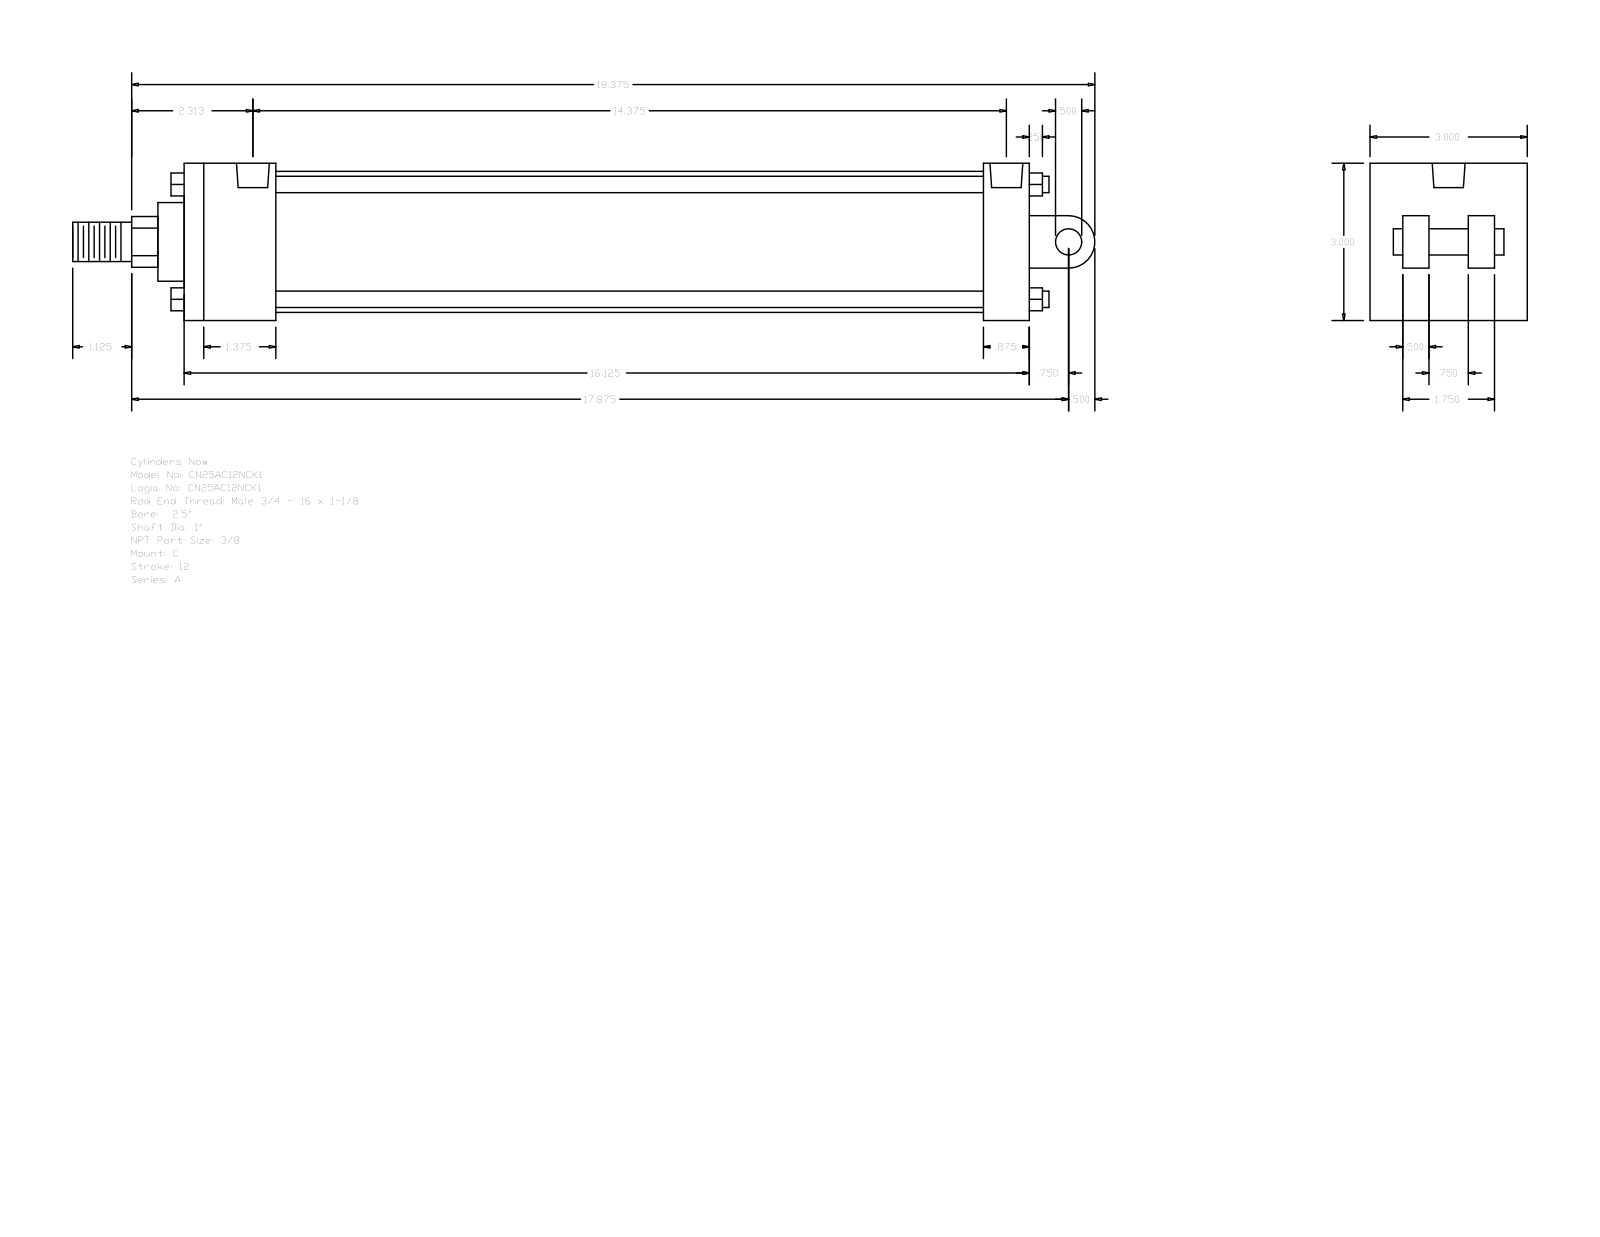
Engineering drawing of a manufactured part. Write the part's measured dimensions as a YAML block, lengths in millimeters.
part_name: "A_C__0250_1"
step_written_by: "GSSL Pune (CONFIG_CONTROL_DESIGN)"
units: millimeters
bodies: {solids: 0, faces: 135, planar: 102, cylindrical: 33, other: 0}
overall_size: [495.3, 76.2, 76.2]
round_holes:
  - {diameter: 5.56, count: 4}
  - {diameter: 15.93, count: 2}
round_bosses_or_shafts:
  - {diameter: 7.94, count: 4}
  - {diameter: 68.33, count: 1}
  - {diameter: 38.1, count: 1}
  - {diameter: 25.4, count: 1}
  - {diameter: 19.05, count: 1}
  - {diameter: 12.7, count: 1}
partial_cylinders:
  - {radius: 12.29, count: 1}
  - {radius: 12.7, count: 1}
face_to_face_distances: [76.2, 409.58, 12.7, 44.45, 387.35, 342.9, 365.13, 22.23, 15.87, 25.4]
hole_center_spacings: [2.38, 367.5, 369.88, 365.12]
